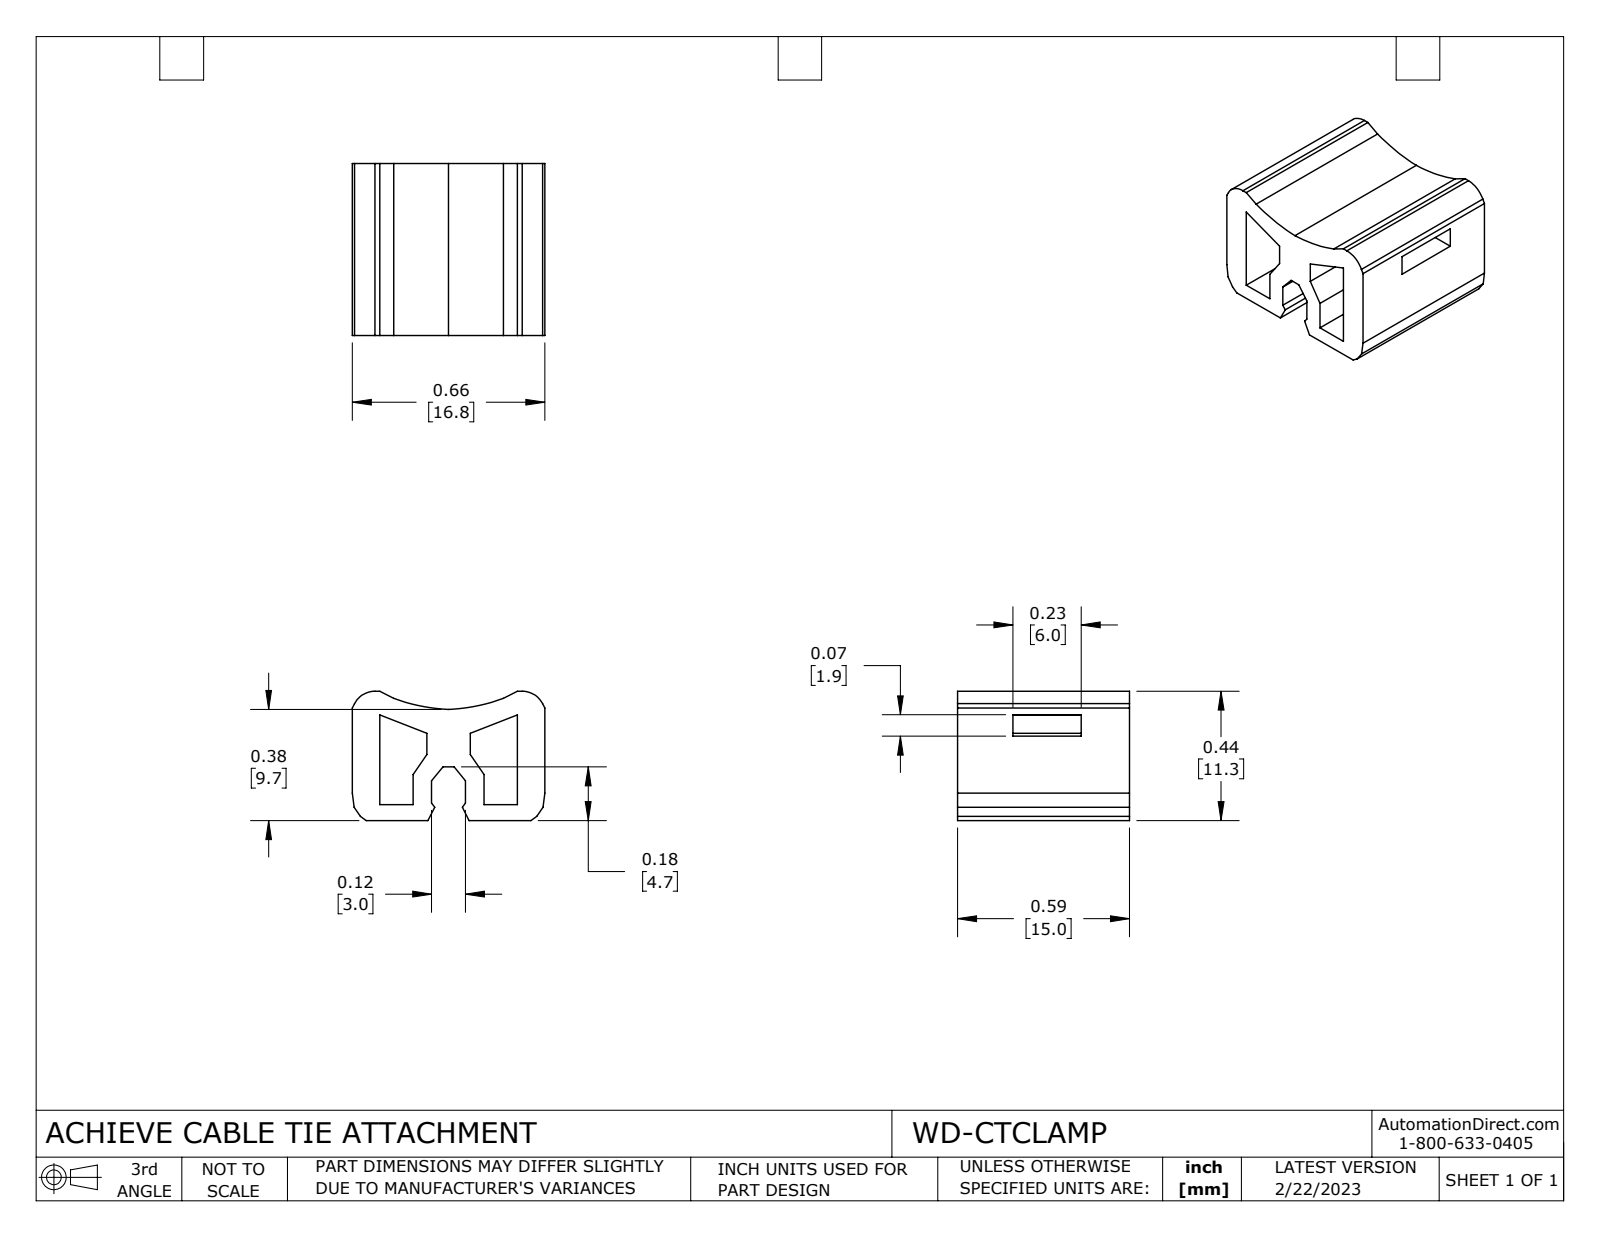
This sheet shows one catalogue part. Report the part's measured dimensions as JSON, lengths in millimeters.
{"part_name": "WD-CTCLAMP", "step_written_by": "SolidWorks 2021 (CONFIG_CONTROL_DESIGN)", "units": "millimeters", "bodies": {"solids": 1, "faces": 53, "planar": 49, "cylindrical": 4, "other": 0}, "overall_size": [16.8, 15, 11.3], "volume_mm3": 1600, "surface_area_mm2": 1829, "partial_cylinders_radius": [[2, 2], [15.1, 2]], "face_to_face_distances": [2.4, 14.4, 15, 12, 16.8, 1.4, 5.3, 11.5, 2.9, 9.1]}
